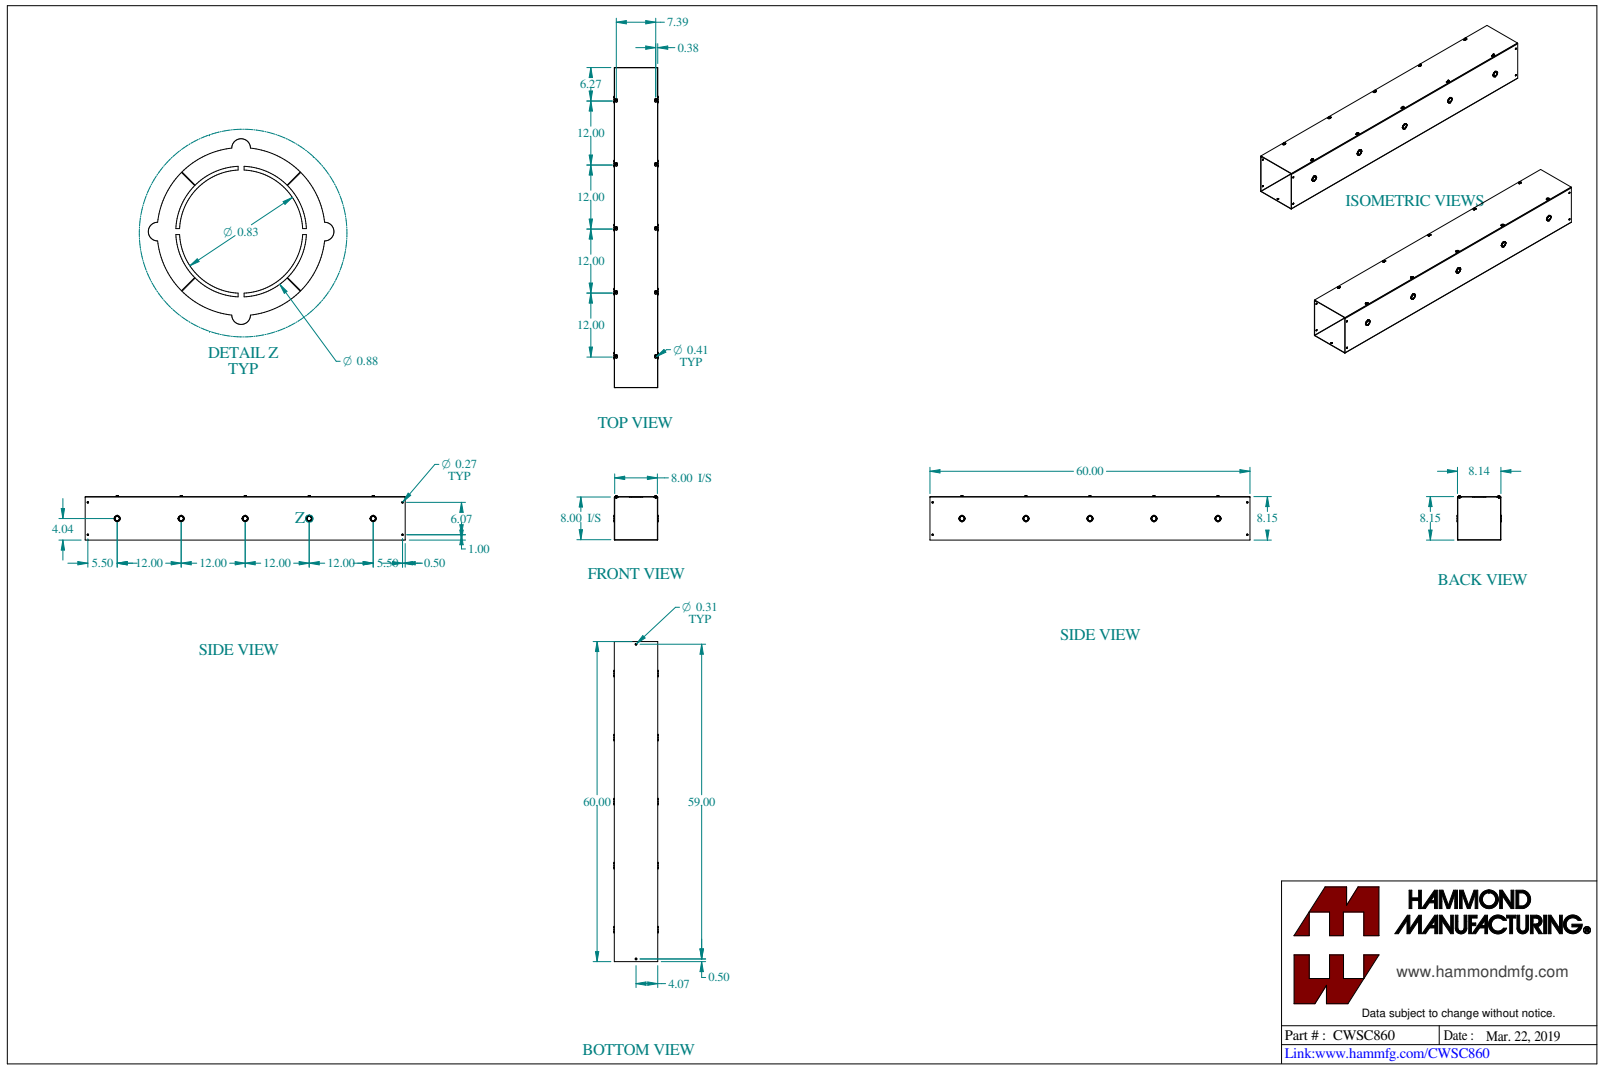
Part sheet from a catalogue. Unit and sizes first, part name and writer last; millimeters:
Units: millimetres
Overall size (bounding box): 1524 × 211.5 × 210.5
Round holes (diameter × count): ⌀4.5 ×10, ⌀22.2 ×5, ⌀6.8 ×4, ⌀8 ×2
Round bosses / shafts (diameter × count): ⌀9.5 ×10, ⌀4.8 ×10, ⌀28.6 ×5, ⌀21 ×5
Partial cylindrical surfaces — rounded edges, fillets, slot ends (radius × count): R1.6 ×20, R3.2 ×10, R5.2 ×10, R0.9 ×4, R2.7 ×4
Main face-to-face distances: 1.8, 205, 203.2, 2, 206.9, 207, 205.2, 201.4, 3.8, 0.8
Hole centre spacings: 304.8, 609.6, 358, 637.9, 914.4, 187.8, 159.6, 168.3
Volume: 2 425 000 mm³ · Surface area: 2 608 000 mm²
Bodies: 12 solids, 786 faces (348 planar, 378 cylindrical, 60 other)
Part name (STEP PRODUCT): CWSC860
STEP written by: SolidWorks 2023 (CONFIG_CONTROL_DESIGN)
